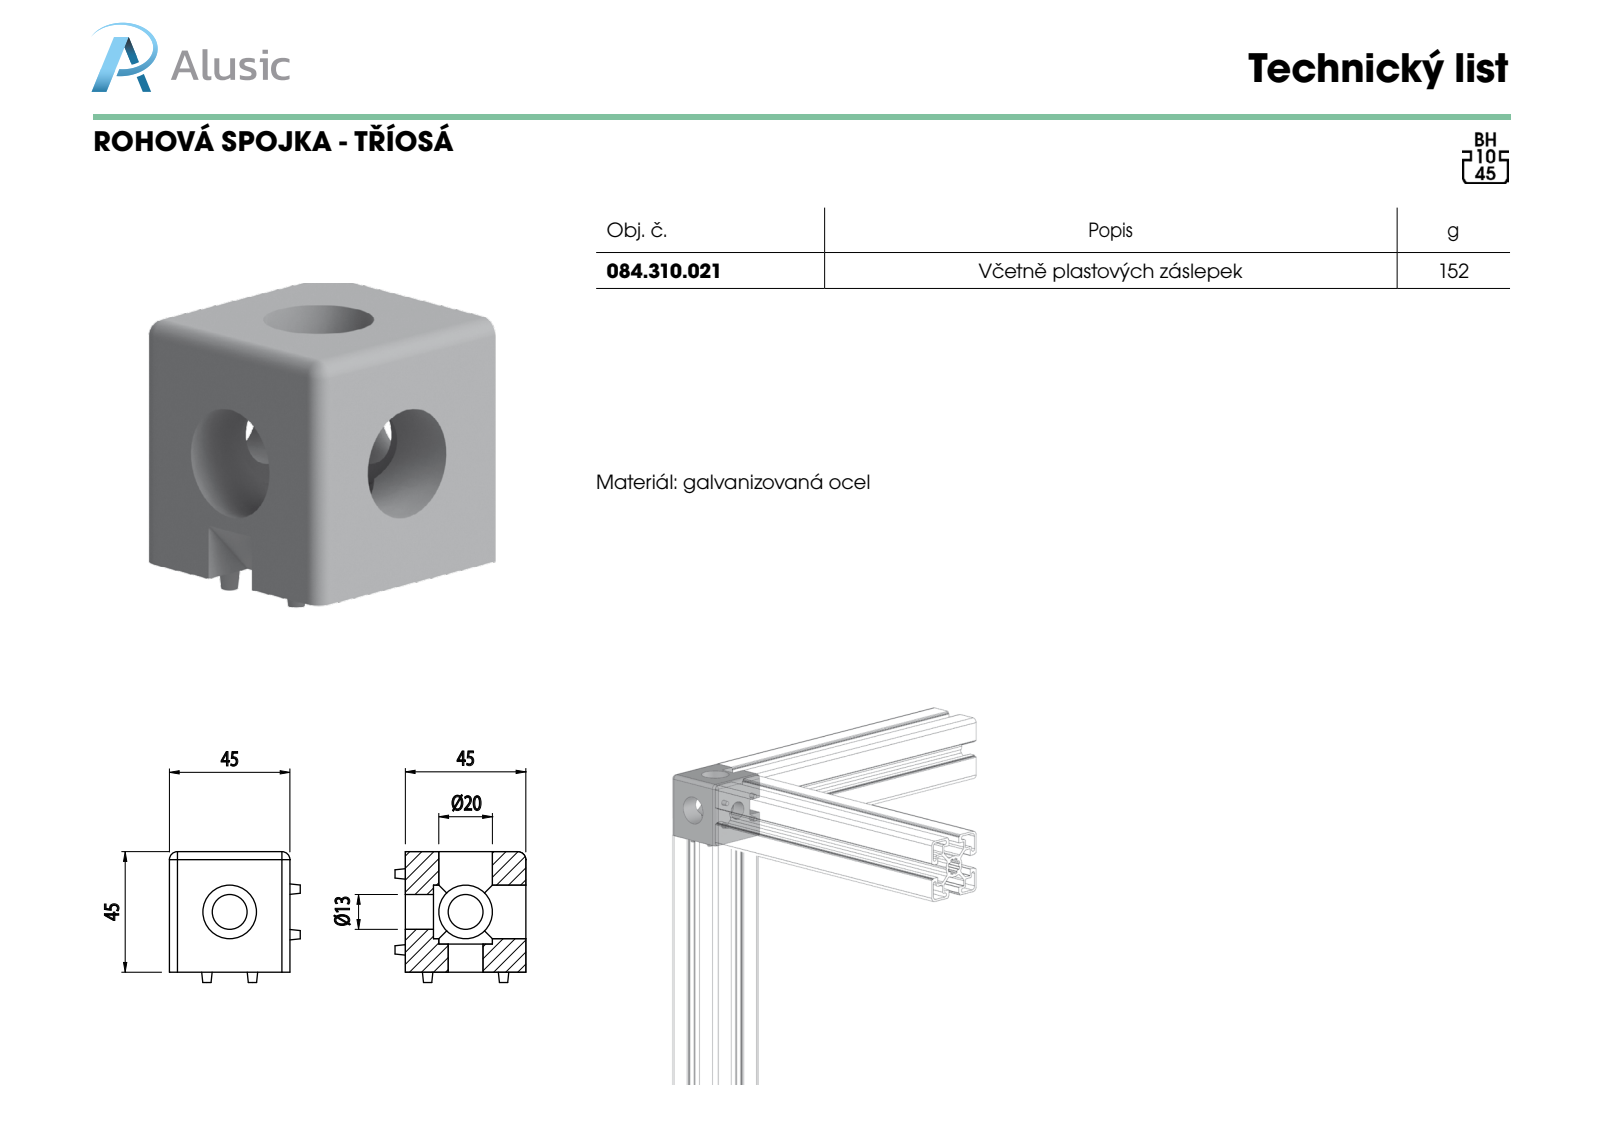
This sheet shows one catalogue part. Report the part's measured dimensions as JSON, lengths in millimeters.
{"part_name": "084.310.021", "step_written_by": "SolidWorks 2011 (CONFIG_CONTROL_DESIGN)", "units": "millimeters", "bodies": {"solids": 1, "faces": 79, "planar": 30, "cylindrical": 23, "other": 26}, "overall_size": [48.85, 48.85, 48.85], "volume_mm3": 64144, "surface_area_mm2": 16008, "round_holes": [[13, 3], [20, 3]], "partial_cylinders_radius": [[3, 5]], "face_to_face_distances": [45, 34.5, 10.5, 17, 28, 17.5, 6.5, 11, 48.85, 14.35]}
